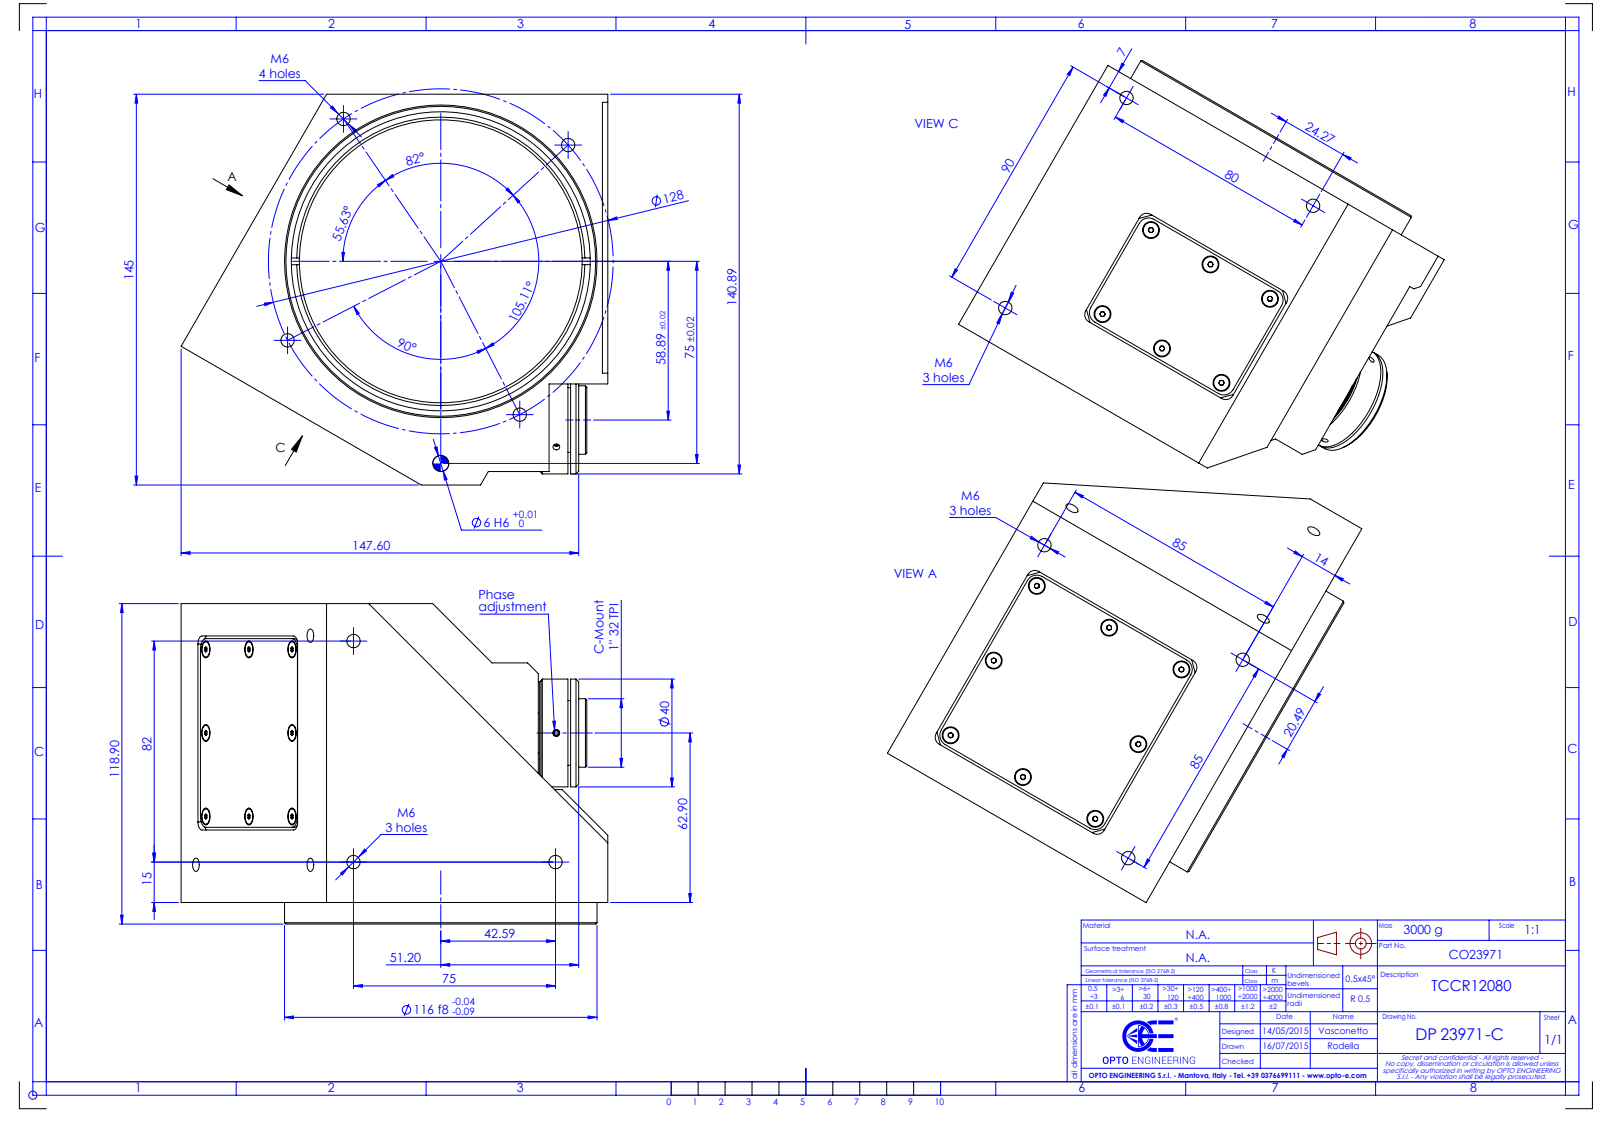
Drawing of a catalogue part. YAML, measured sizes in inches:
part_name: "DP23971_TCCR12080"
step_written_by: "SolidWorks 2021 (CONFIG_CONTROL_DESIGN)"
units: inches
bodies: {solids: 0, faces: 321, planar: 121, cylindrical: 110, other: 90}
overall_size: [6.237, 5.709, 4.681]
round_holes:
  - {diameter: 0.197, count: 13}
  - {diameter: 0.098, count: 3}
  - {diameter: 0.071, count: 2}
  - {diameter: 0.236, count: 1}
  - {diameter: 0.571, count: 1}
  - {diameter: 0.866, count: 1}
  - {diameter: 0.886, count: 1}
  - {diameter: 4.134, count: 1}
  - {diameter: 4.37, count: 1}
round_bosses_or_shafts:
  - {diameter: 0.226, count: 16}
  - {diameter: 4.567, count: 1}
  - {diameter: 1.575, count: 1}
  - {diameter: 1.504, count: 1}
  - {diameter: 1.488, count: 1}
  - {diameter: 1, count: 1}
partial_cylinders:
  - {radius: 0.157, count: 10}
  - {radius: 0.118, count: 8}
face_to_face_distances: [0.02, 4.366, 5.709, 4.075, 1.634, 1.016, 0.157, 0.197, 0.472, 0.039]
hole_center_spacings: [2.52, 0.394, 2.953, 3.346, 0.787, 1.357, 1.886, 2.519]
